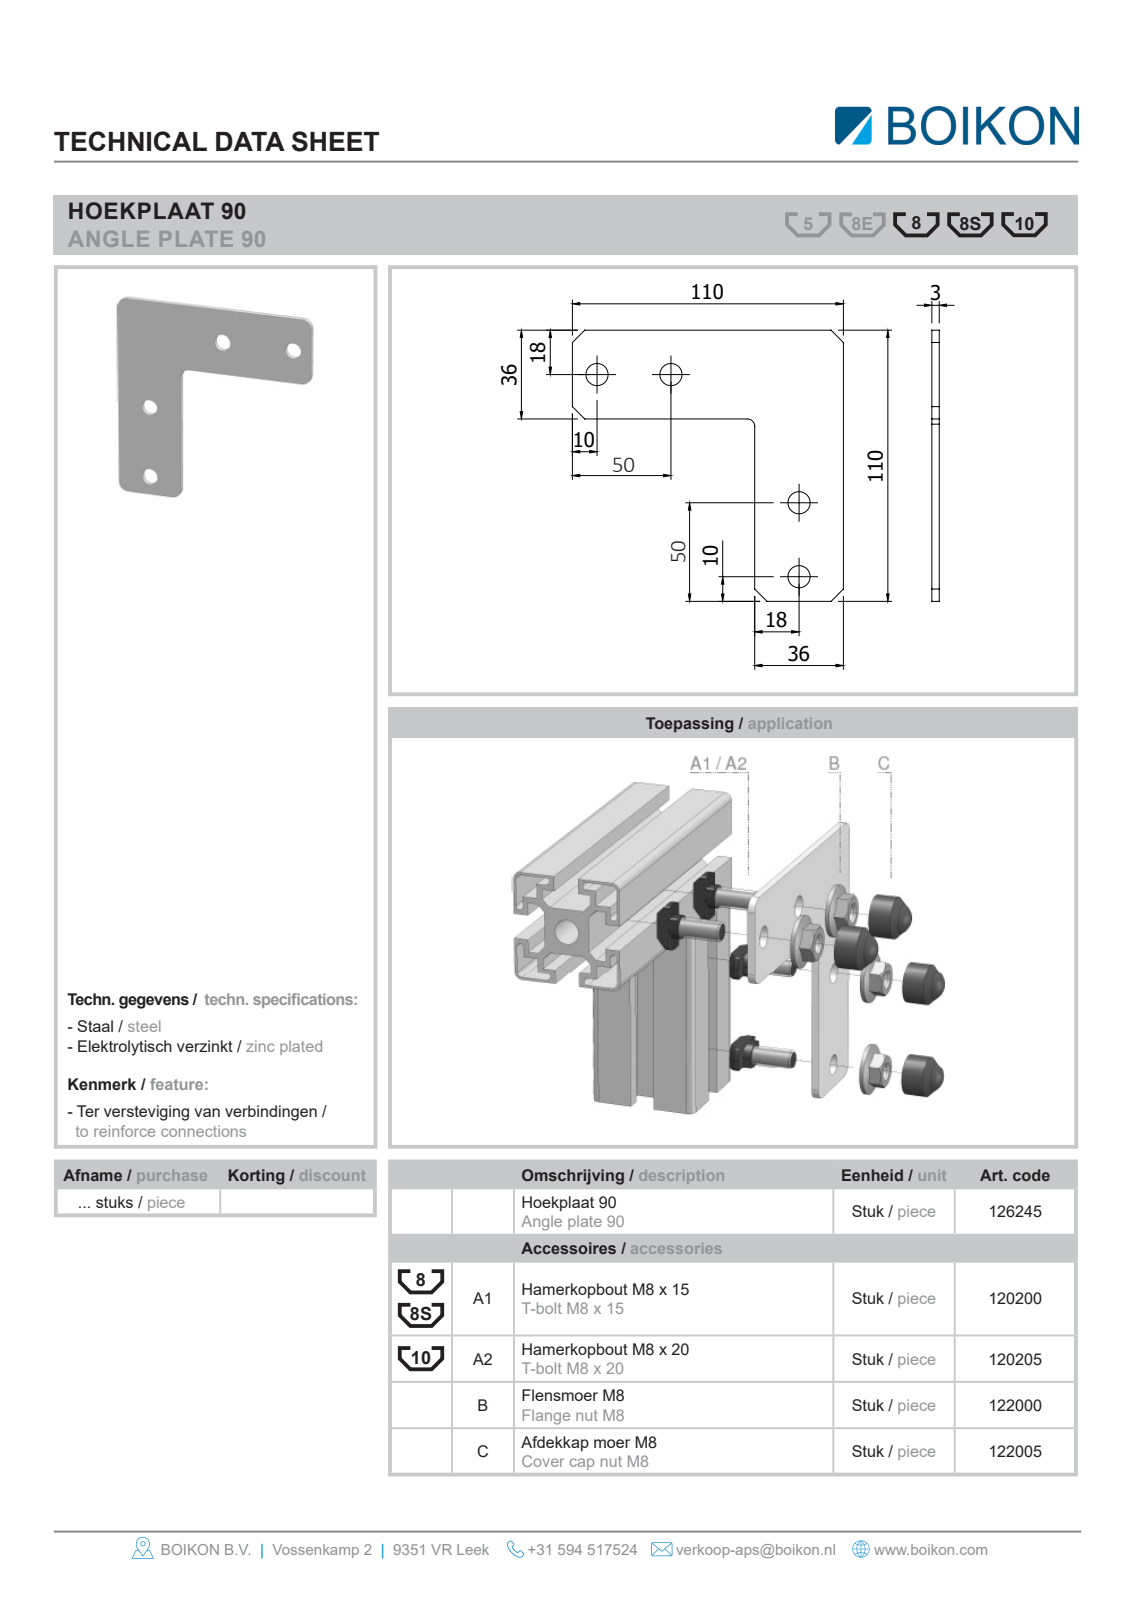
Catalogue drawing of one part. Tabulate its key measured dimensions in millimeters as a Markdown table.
| quantity | value |
| --- | --- |
| part name | Root; 126245 Hoekplaat 90BOIKON; 122000Flensmoer M8BOIKON; 122005Afdekkap voor moer M8BOIKON (+1 more) |
| STEP written by | HiCAD 2013 1802.4 Build 509 (AUTOMOTIVE_DESIGN) |
| units | millimeters |
| bodies | 13 solids, 370 faces (252 planar, 66 cylindrical, 52 other) |
| overall size | 110.5 × 110.5 × 30.8 |
| volume | 38 563 mm³ |
| surface area | 28 040 mm² |
| round holes (diameter × count) | 8 × 4, 9 × 4 |
| round bosses / shafts (diameter × count) | 21 × 4, 16.8 × 4, 6.47 × 4 |
| partial cylindrical surfaces (radius × count) | 1 × 20, 5 × 14, 1.16 × 4, 9.5 × 4 |
| main face-to-face distances | 3, 13, 7, 11.5, 5.5, 10, 4.5, 34.64, 24.5, 10.3 |
| hole center spacings | 40, 92.13, 59.4, 115.97 |
